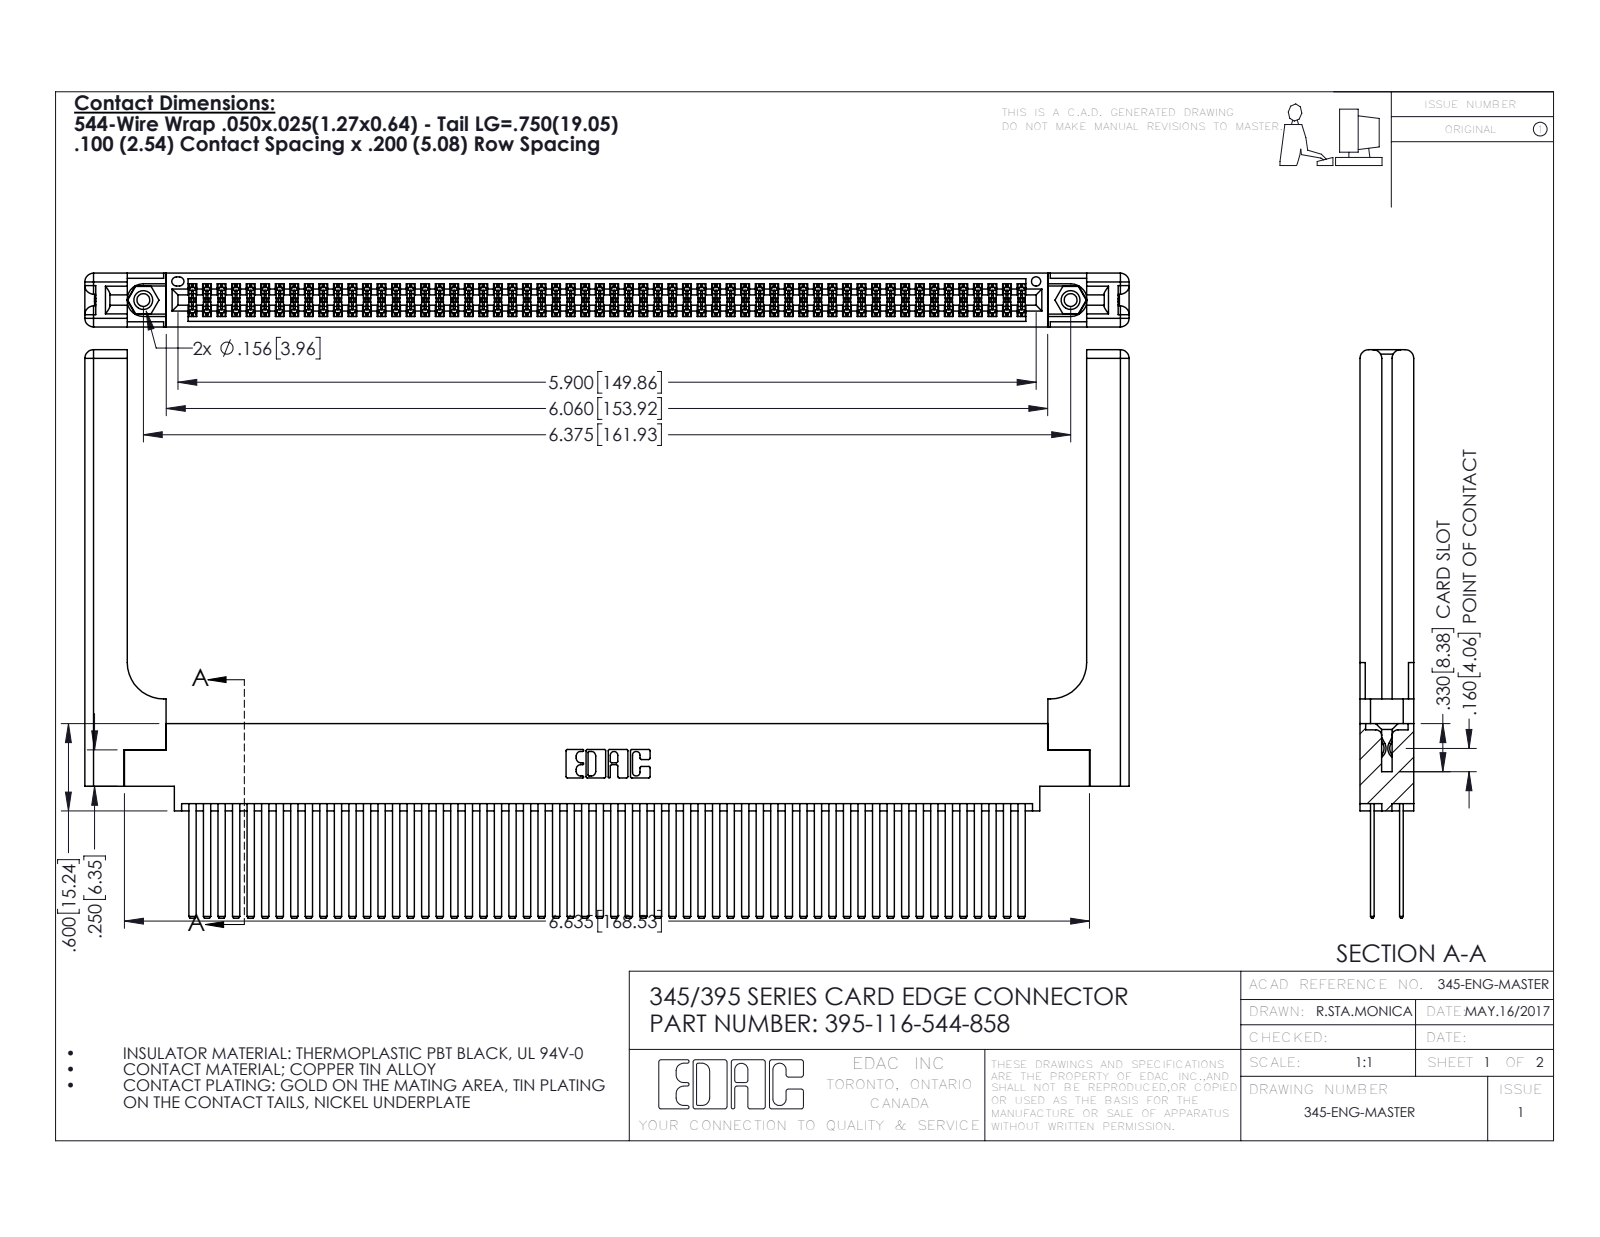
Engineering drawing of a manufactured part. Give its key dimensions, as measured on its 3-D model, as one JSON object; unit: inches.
{"part_name": "345-292-001_345-293-144; 345-220-058_345-220-058; 345 Part_0.170 Offset - 0.156 Dia-TH; 345-250-001_345-250-001-102 (+1 more)", "step_written_by": "SolidWorks 2016 (CONFIG_CONTROL_DESIGN)", "units": "inches", "bodies": {"solids": 121, "faces": 5490, "planar": 3596, "cylindrical": 1834, "other": 60}, "overall_size": [7.179, 3.907, 0.37], "volume_in3": 1.699, "surface_area_in2": 60.32, "round_holes": [[0.089, 2], [0.125, 2], [0.156, 2], [0.064, 1]], "round_bosses_or_shafts": [[0.155, 2]], "partial_cylinders_radius": [[0.006, 174], [0.01, 22], [0.06, 16], [0.007, 6], [0.031, 6], [0.026, 3], [0.014, 2], [0.019, 2]], "face_to_face_distances": [0.072, 0.298, 0.098, 0.272, 0.025, 0.2, 0.37, 0.225, 0.175, 0.148], "hole_center_spacings": [0.27, 6.139, 6.375]}
